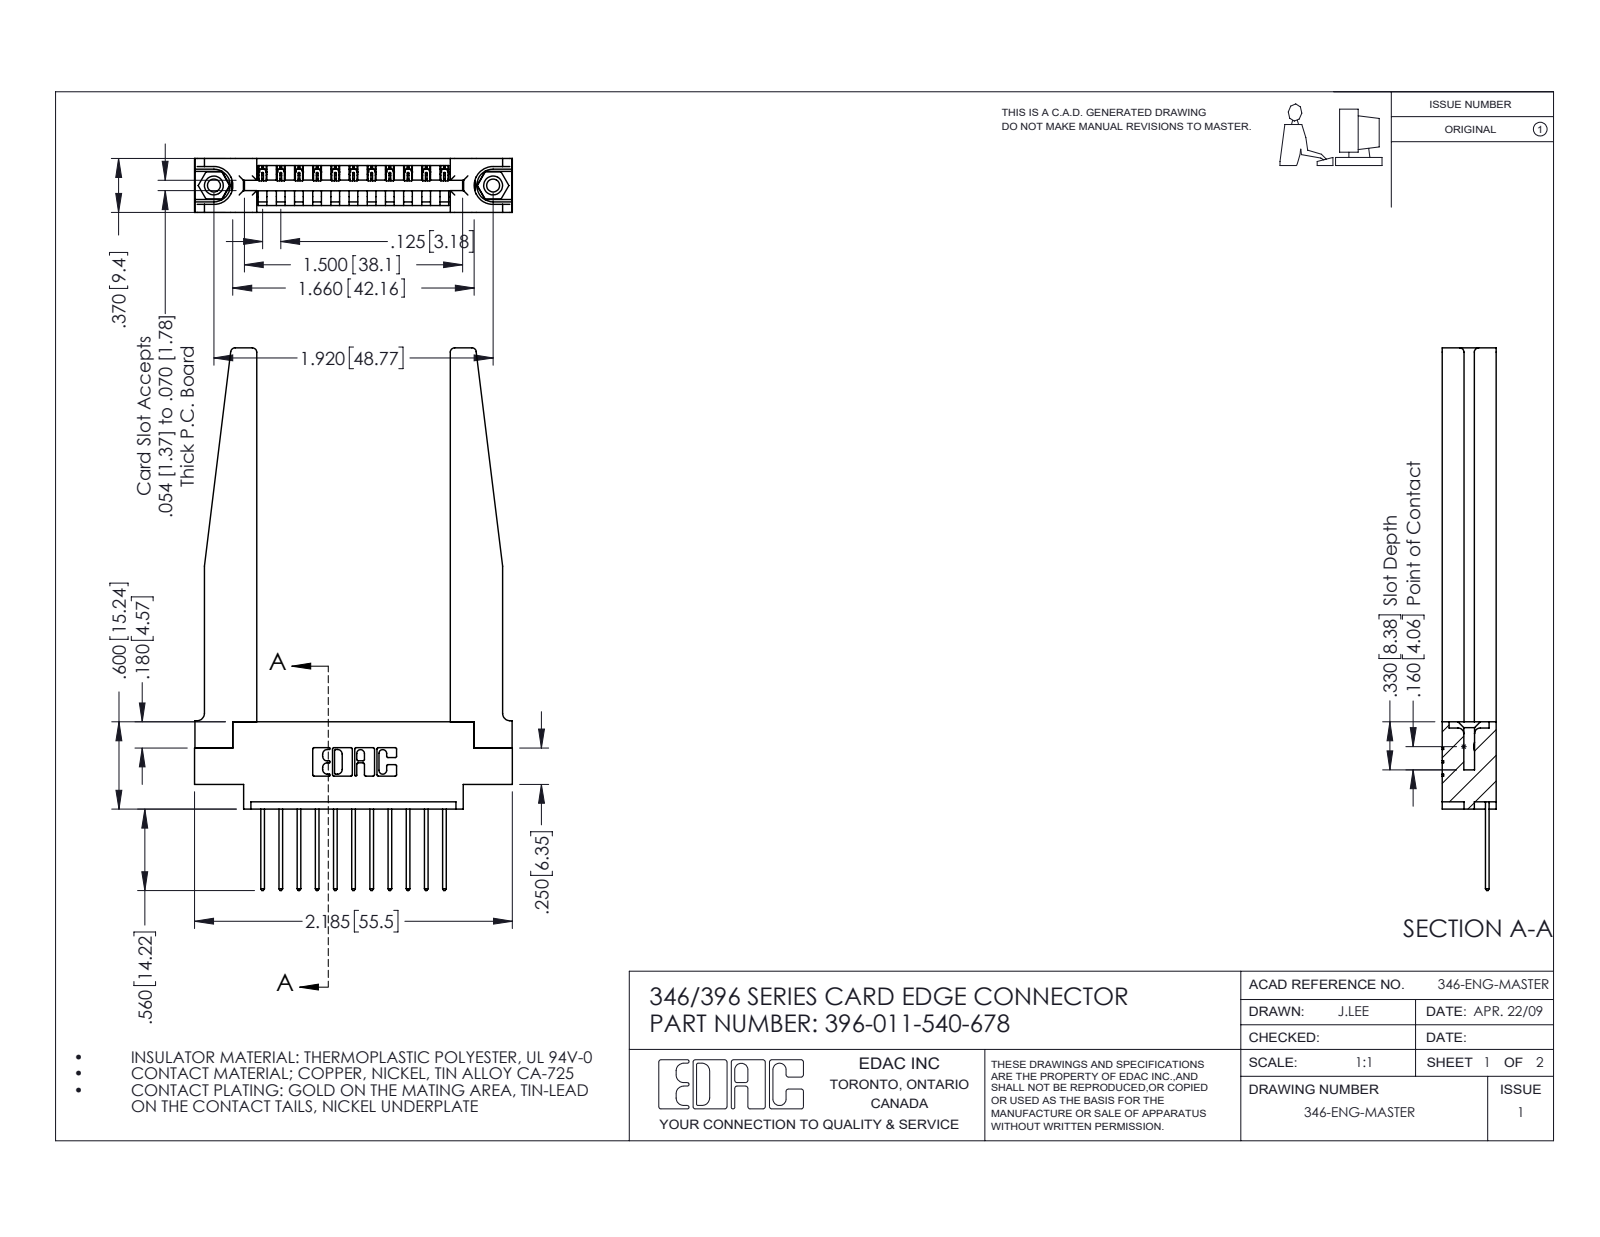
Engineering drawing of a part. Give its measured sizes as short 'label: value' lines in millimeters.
name: 396-011-540-678; 345-250-001_345-250-001-102; 345-292-001_345-293-140; 346 Part_0.170 Offset - 0.156 Dia-TH (+1 more)
written by: SolidWorks 2016 (CONFIG_CONTROL_DESIGN)
unit: mm
bodies: 16 solids, 998 faces (662 planar, 284 cylindrical, 52 other)
size: 94.7 × 55.5 × 9.4
volume: 11 900 mm³; area: 12 670 mm²
holes: 2× ⌀2.3, 2× ⌀3.2, 2× ⌀4, 1× ⌀1.6
bosses: 2× ⌀3.9
rounds: 22× R0.2, 22× R0.3, 22× R0.3, 8× R0.8, 6× R0.2, 6× R0.8, 3× R0.7, 2× R0.8
face distances: 9.4, 3.8, 1.8, 3.8, 1.2, 8.2, 6.4, 5.6, 2.6, 4.4
hole spacings: 6.2, 43.6, 48.8
